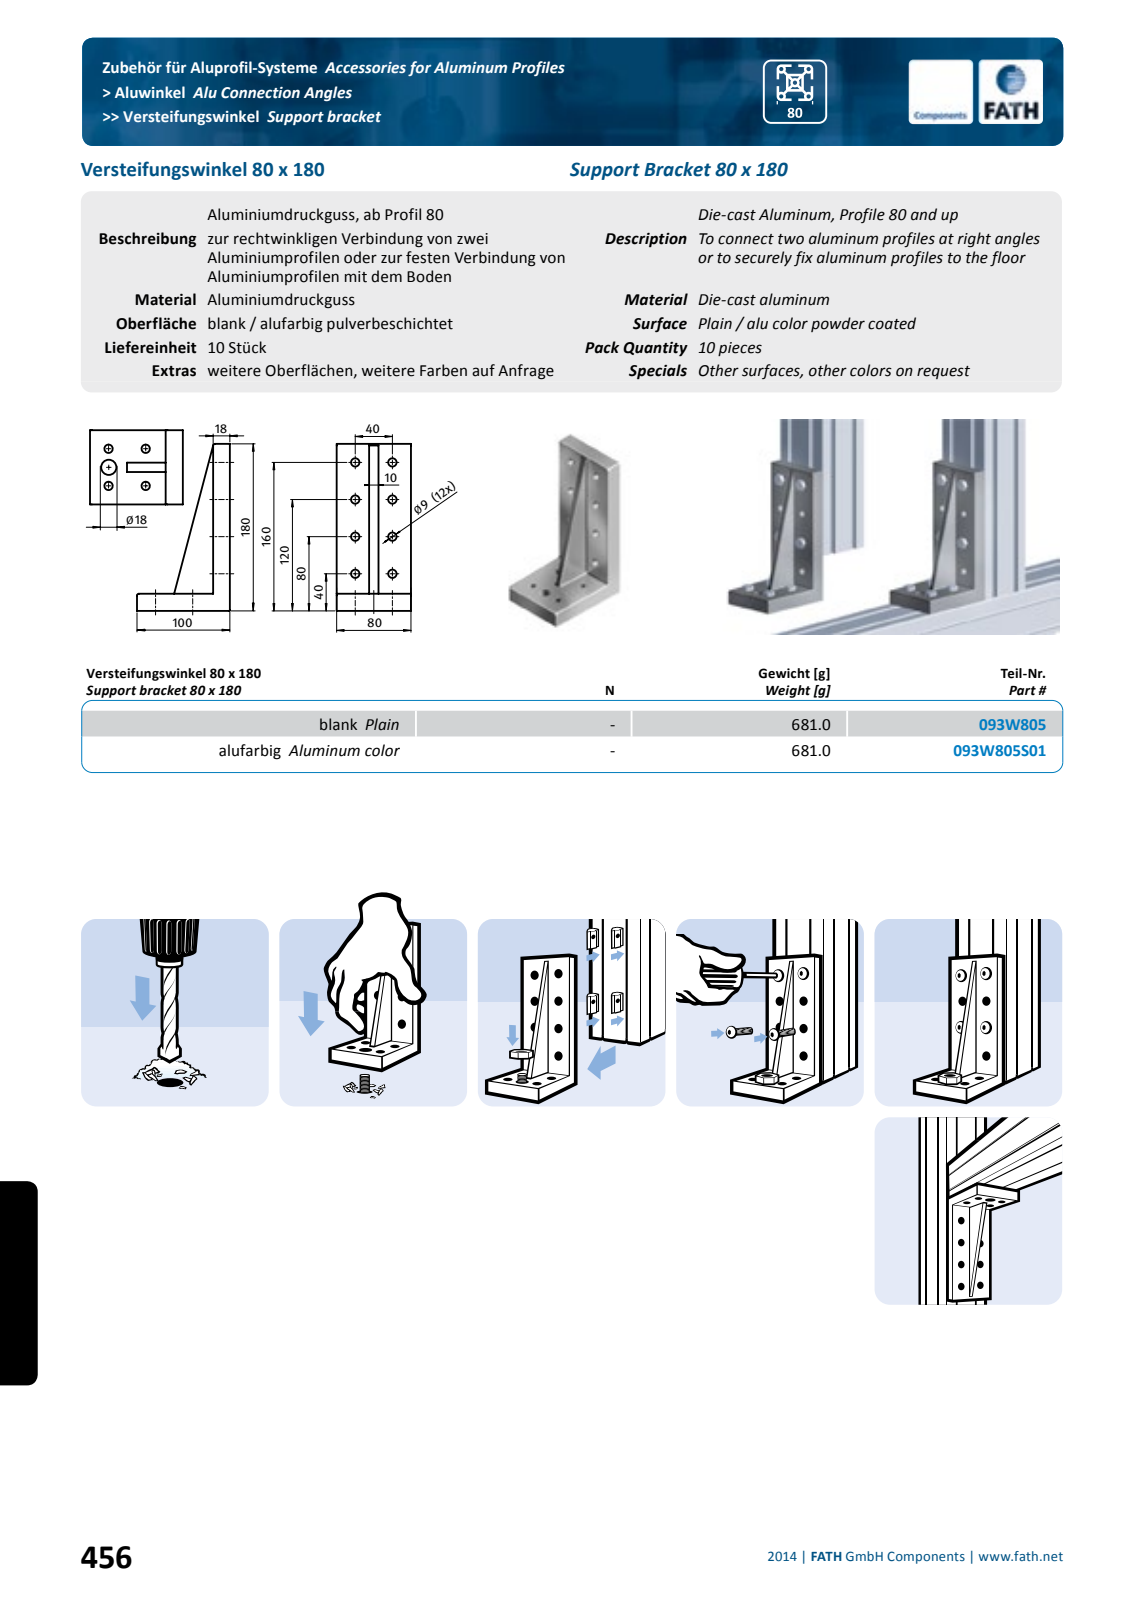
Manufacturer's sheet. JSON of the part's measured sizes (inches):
{"part_name": "fath_093w805", "step_written_by": "Spatial InterOp 3D (automotive_design)", "units": "inches", "bodies": {"solids": 1, "faces": 423, "planar": 98, "cylindrical": 114, "other": 211}, "overall_size": [7.087, 3.937, 3.149], "volume_in3": 15.51, "surface_area_in2": 127.6, "partial_cylinders_radius": [[0.02, 59], [0.079, 18], [0.039, 1]], "face_to_face_distances": [0.472, 0.236, 0.709, 1.573, 1.114, 3.146, 7.087, 6.614, 3.937, 3.465]}
